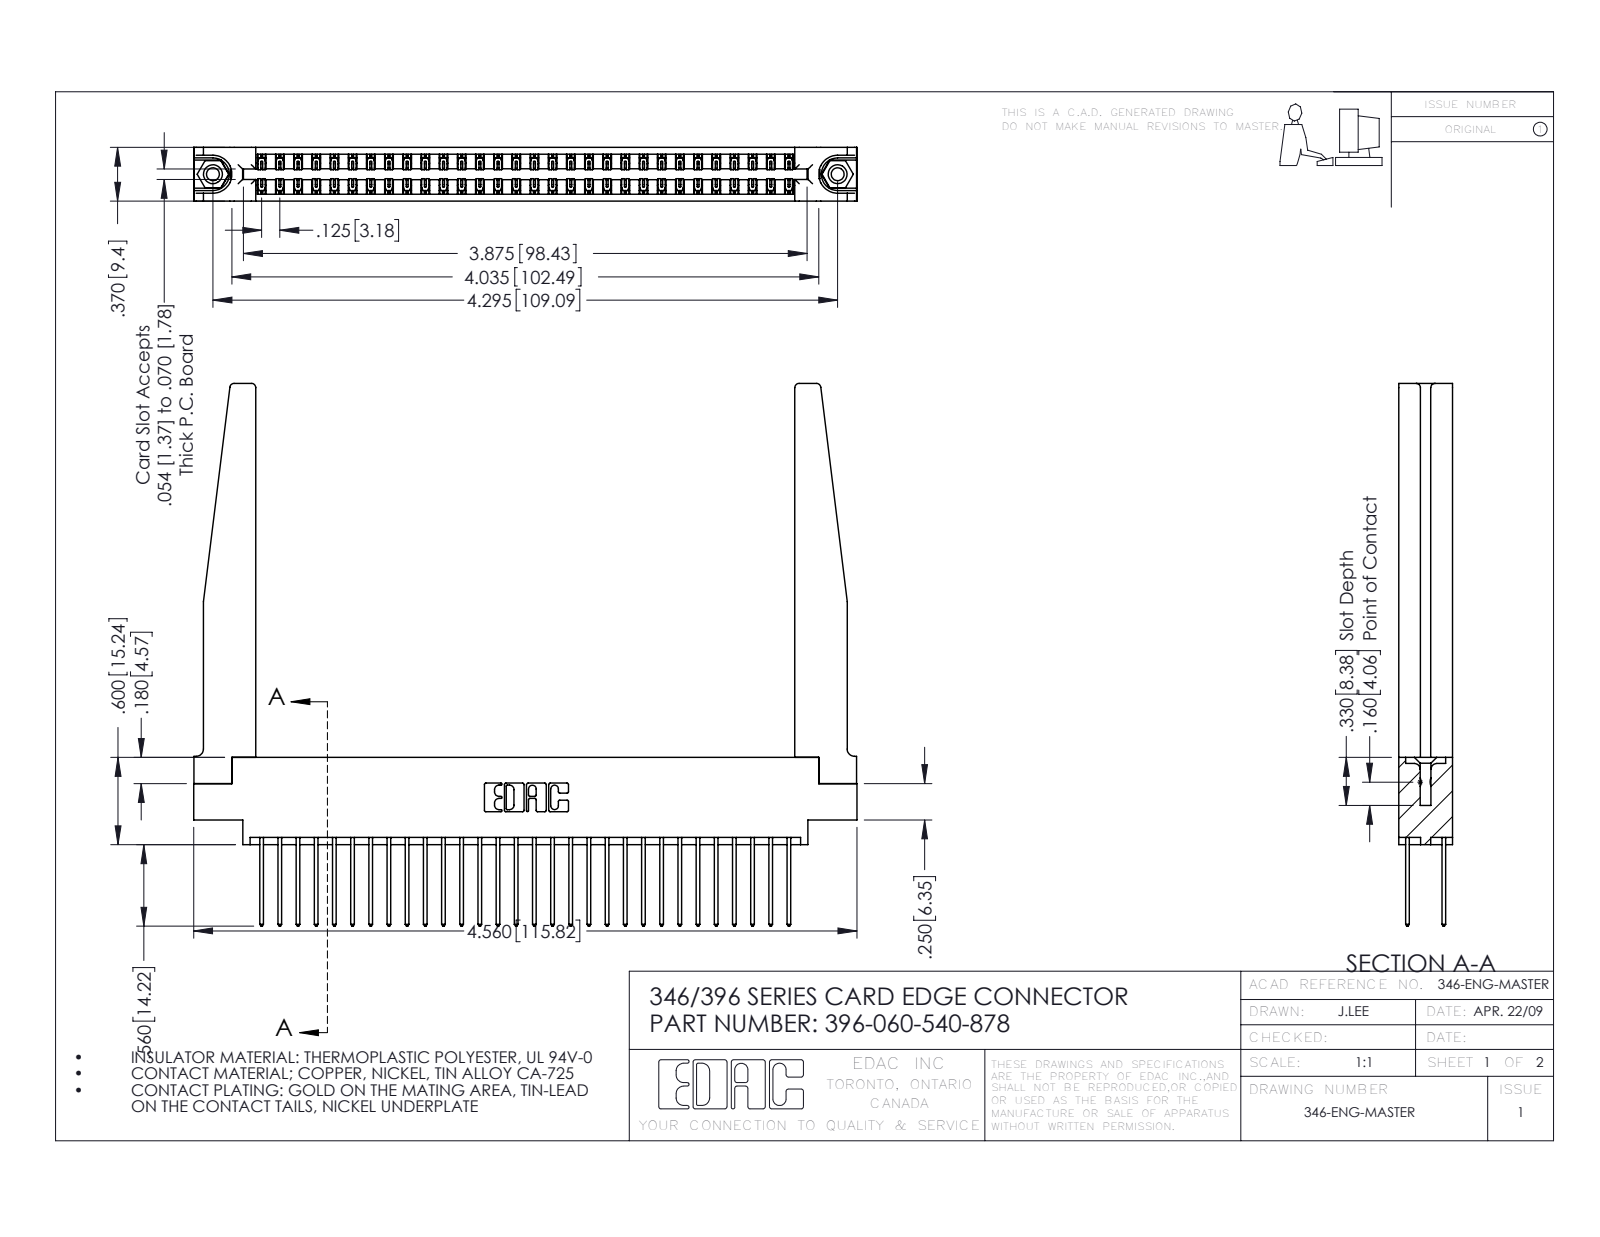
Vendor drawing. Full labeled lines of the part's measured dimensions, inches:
Part name (STEP PRODUCT): 345-292-001_345-293-140; 396-060-540-878; 345-250-001_345-250-001-102; 346-220-078_345-220-078 (+1 more)
STEP written by: SolidWorks 2016 (CONFIG_CONTROL_DESIGN)
Units: inches
Bodies: 65 solids, 3480 faces (2322 planar, 1106 cylindrical, 52 other)
Overall size (bounding box): 4.56 × 3.73 × 0.37
Volume: 1.11 in³ · Surface area: 35.81 in²
Round holes (diameter × count): ⌀0.089 ×2, ⌀0.125 ×2, ⌀0.156 ×2, ⌀0.064 ×1
Round bosses / shafts (diameter × count): ⌀0.155 ×2
Partial cylindrical surfaces — rounded edges, fillets, slot ends (radius × count): R0.006 ×90, R0.01 ×60, R0.01 ×22, R0.03 ×8, R0.007 ×6, R0.031 ×6, R0.026 ×3, R0.014 ×2
Main face-to-face distances: 0.37, 0.048, 0.322, 0.072, 0.25, 0.298, 0.025, 0.148, 0.15, 0.275
Hole centre spacings: 0.246, 4.087, 4.295
